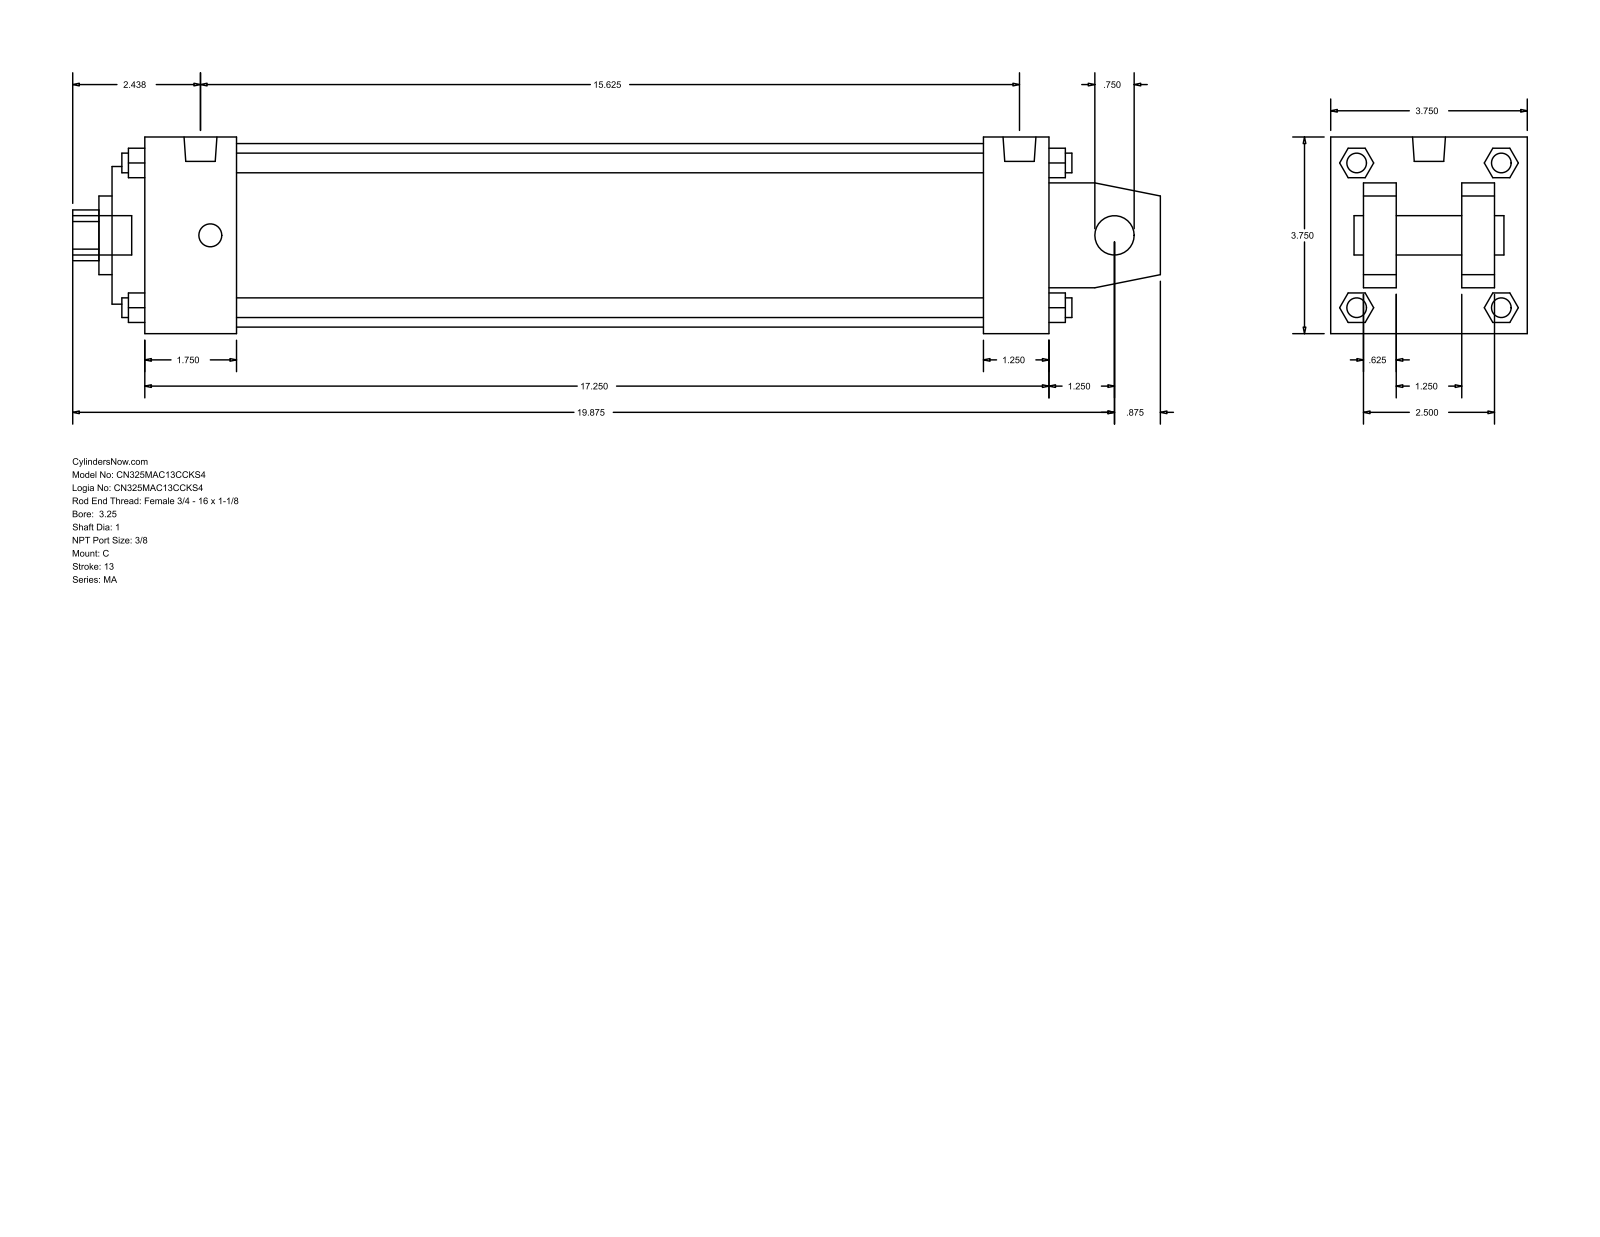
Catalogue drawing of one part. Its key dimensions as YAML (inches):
part_name: "MA_C__0325_1"
step_written_by: "GSSL Pune (CONFIG_CONTROL_DESIGN)"
units: inches
bodies: {solids: 0, faces: 141, planar: 109, cylindrical: 32, other: 0}
overall_size: [20.75, 3.75, 3.75]
round_holes:
  - {diameter: 0.75, count: 1}
  - {diameter: 1, count: 1}
  - {diameter: 1.5, count: 1}
  - {diameter: 2.625, count: 1}
  - {diameter: 3.5, count: 1}
round_bosses_or_shafts:
  - {diameter: 0.437, count: 4}
  - {diameter: 0.375, count: 4}
  - {diameter: 0.627, count: 2}
  - {diameter: 0.75, count: 1}
partial_cylinders:
  - {radius: 0.484, count: 1}
face_to_face_distances: [3.75, 0.625, 2.5, 17.25, 1.25, 3.125, 1.875, 17.875, 16, 1.25]
